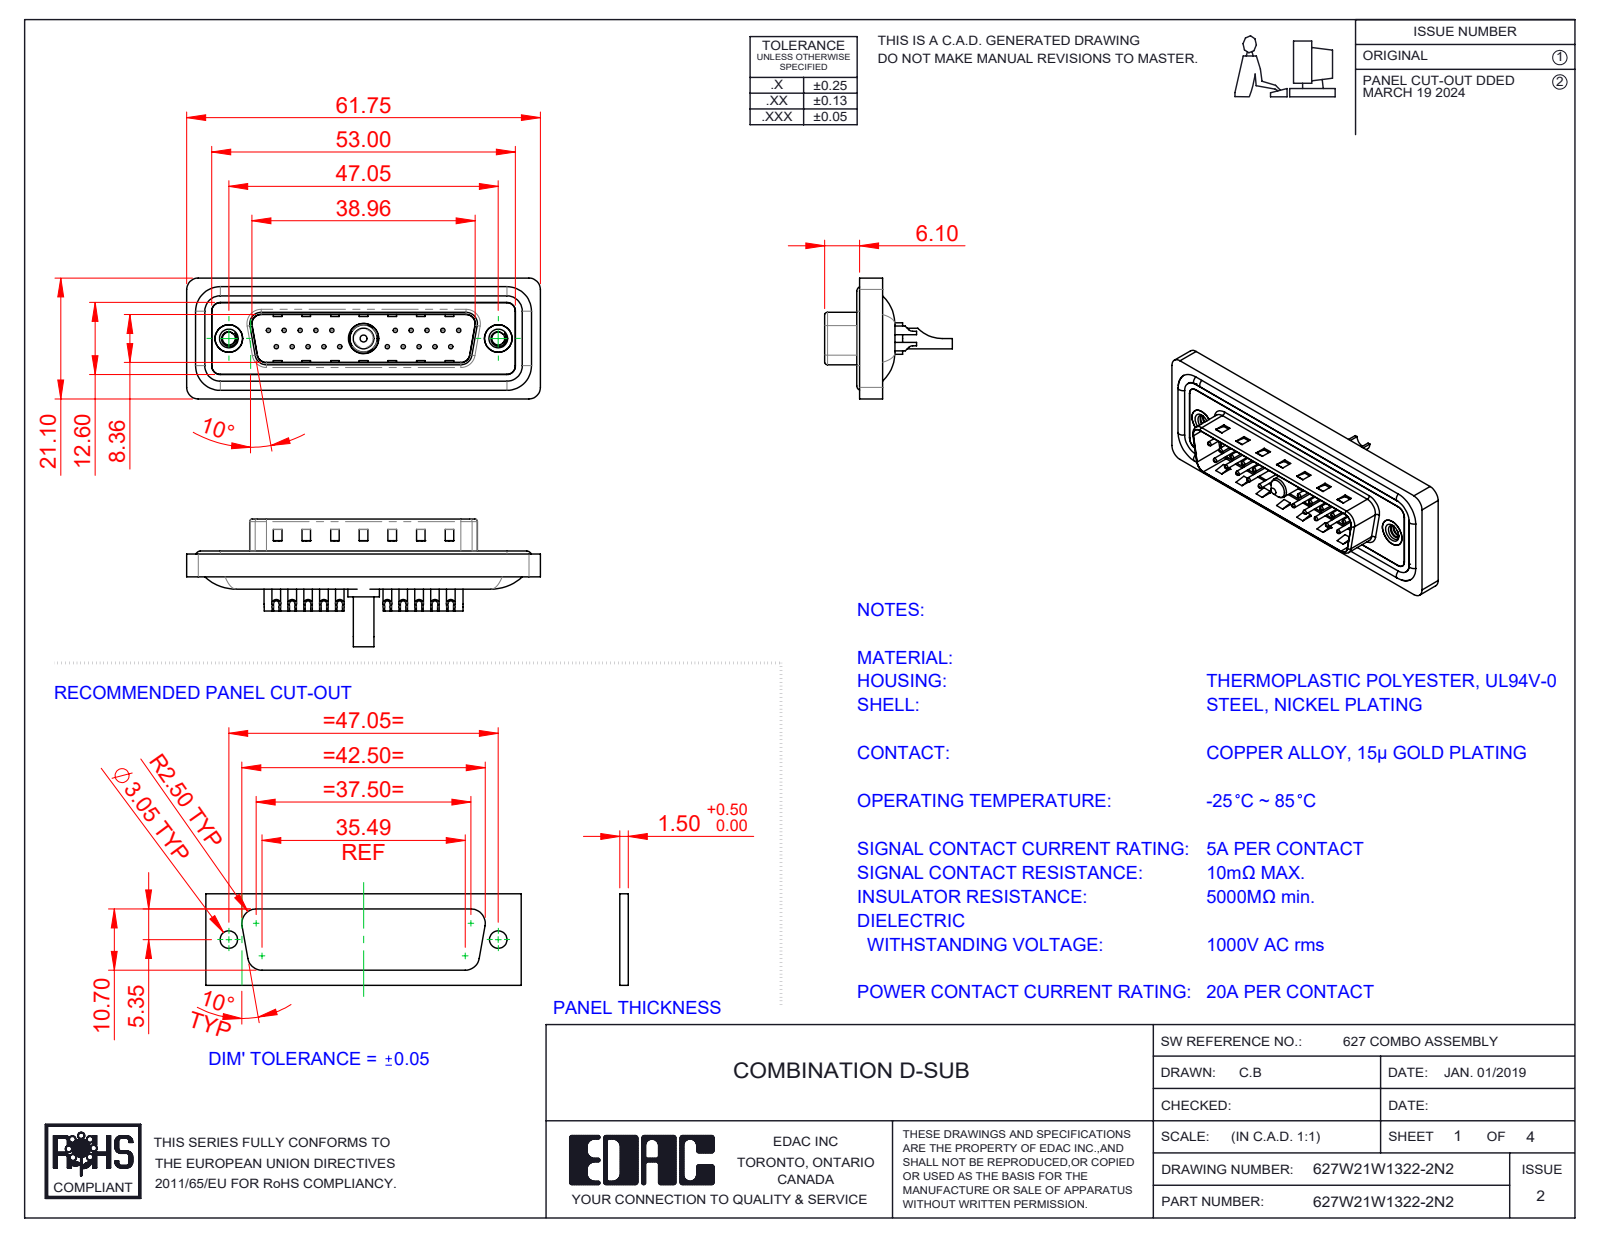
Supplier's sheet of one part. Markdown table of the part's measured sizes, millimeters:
| quantity | value |
| --- | --- |
| part name | 627Combo Contact Row 2_22; 627Combo Shell Front_25 Contacts; Power Pin_20A SC; 627Combo Contact Row 1_22 (+5 more) |
| STEP written by | SolidWorks 2023 (CONFIG_CONTROL_DESIGN) |
| units | millimeters |
| bodies | 29 solids, 1269 faces (402 planar, 530 cylindrical, 337 other) |
| overall size | 61.75 × 22.3 × 21.1 |
| volume | 7 241 mm³ |
| surface area | 12 195 mm² |
| round holes (diameter × count) | 0.75 × 20, 1 × 20, 1.6 × 20, 2 × 20, 2.26 × 2, 4 × 2, 4.8 × 2, 5 × 2, 2.7 × 1, 4.85 × 1, 5.3 × 1 |
| round bosses / shafts (diameter × count) | 1.5 × 20, 1.6 × 4, 4.9 × 2, 5.5 × 1, 5.2 × 1, 4.75 × 1, 3.75 × 1, 3.6 × 1 |
| partial cylindrical surfaces (radius × count) | 1.5 × 22, 2 × 18, 0.5 × 8, 1.6 × 8, 1 × 6, 0.25 × 4, 0.6 × 4, 0.65 × 4 |
| main face-to-face distances | 0.4, 1.5, 1.1, 1.6, 0.5, 3.1, 2.9, 4.1, 0.82, 9.58 |
| hole center spacings | 3.16, 2.77, 5.54, 8.31, 5.04, 19.39, 20.97, 22.16 |
